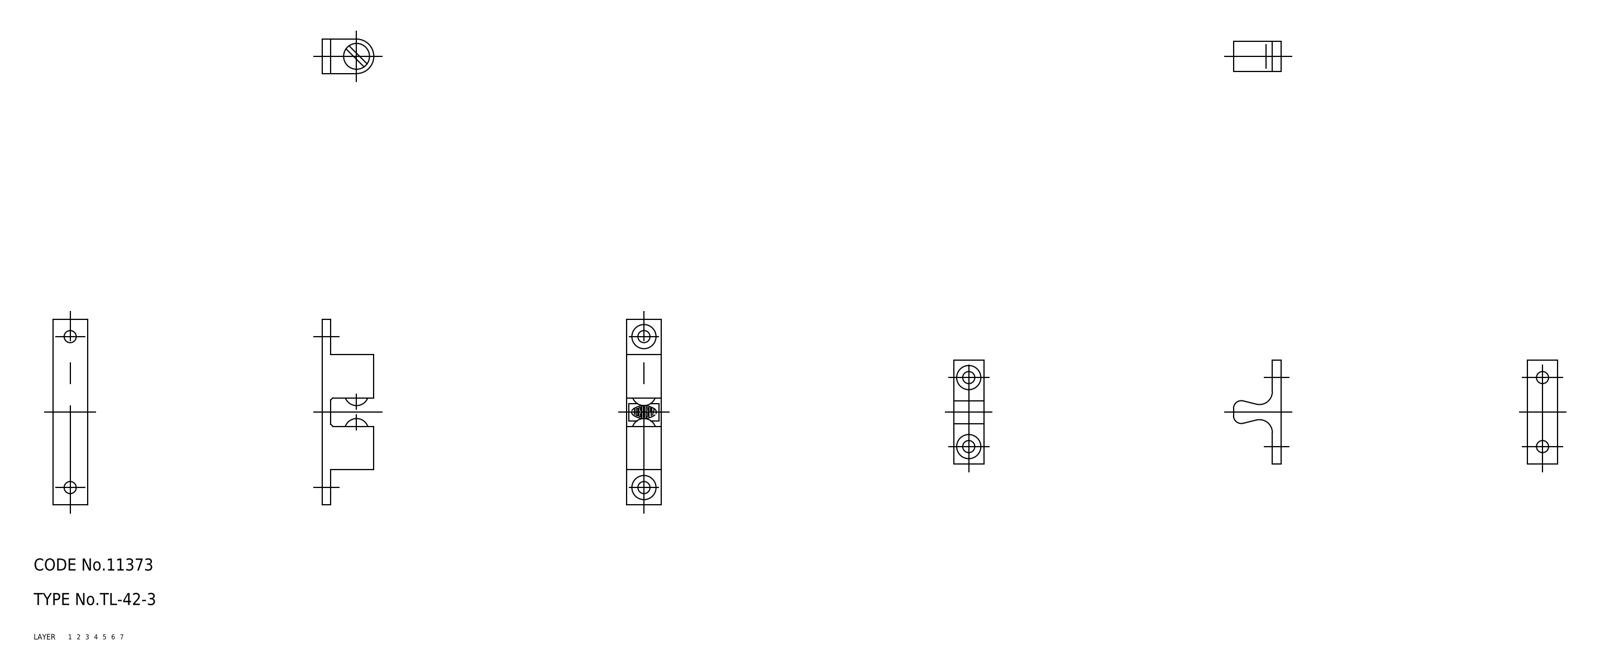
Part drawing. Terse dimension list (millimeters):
name: ball; screw; keeper; housing
written by: spGate 19.8.4 (****-****-****-****) (AUTOMOTIVE_DESIGN)
unit: mm
bodies: 6 solids, 80 faces (34 planar, 26 cylindrical, 20 other)
size: 47.14 × 43 × 8
volume: 2 591 mm³; area: 2 880 mm²
holes: 4× ⌀2.8, 1× ⌀5, 1× ⌀6
rounds: 2× R1.8, 2× R3, 1× R4
face distances: 8, 0.5, 2, 45.14, 7.5, 47.14, 10, 16.6, 7, 4
hole spacings: 9.5, 25.5, 16, 35
